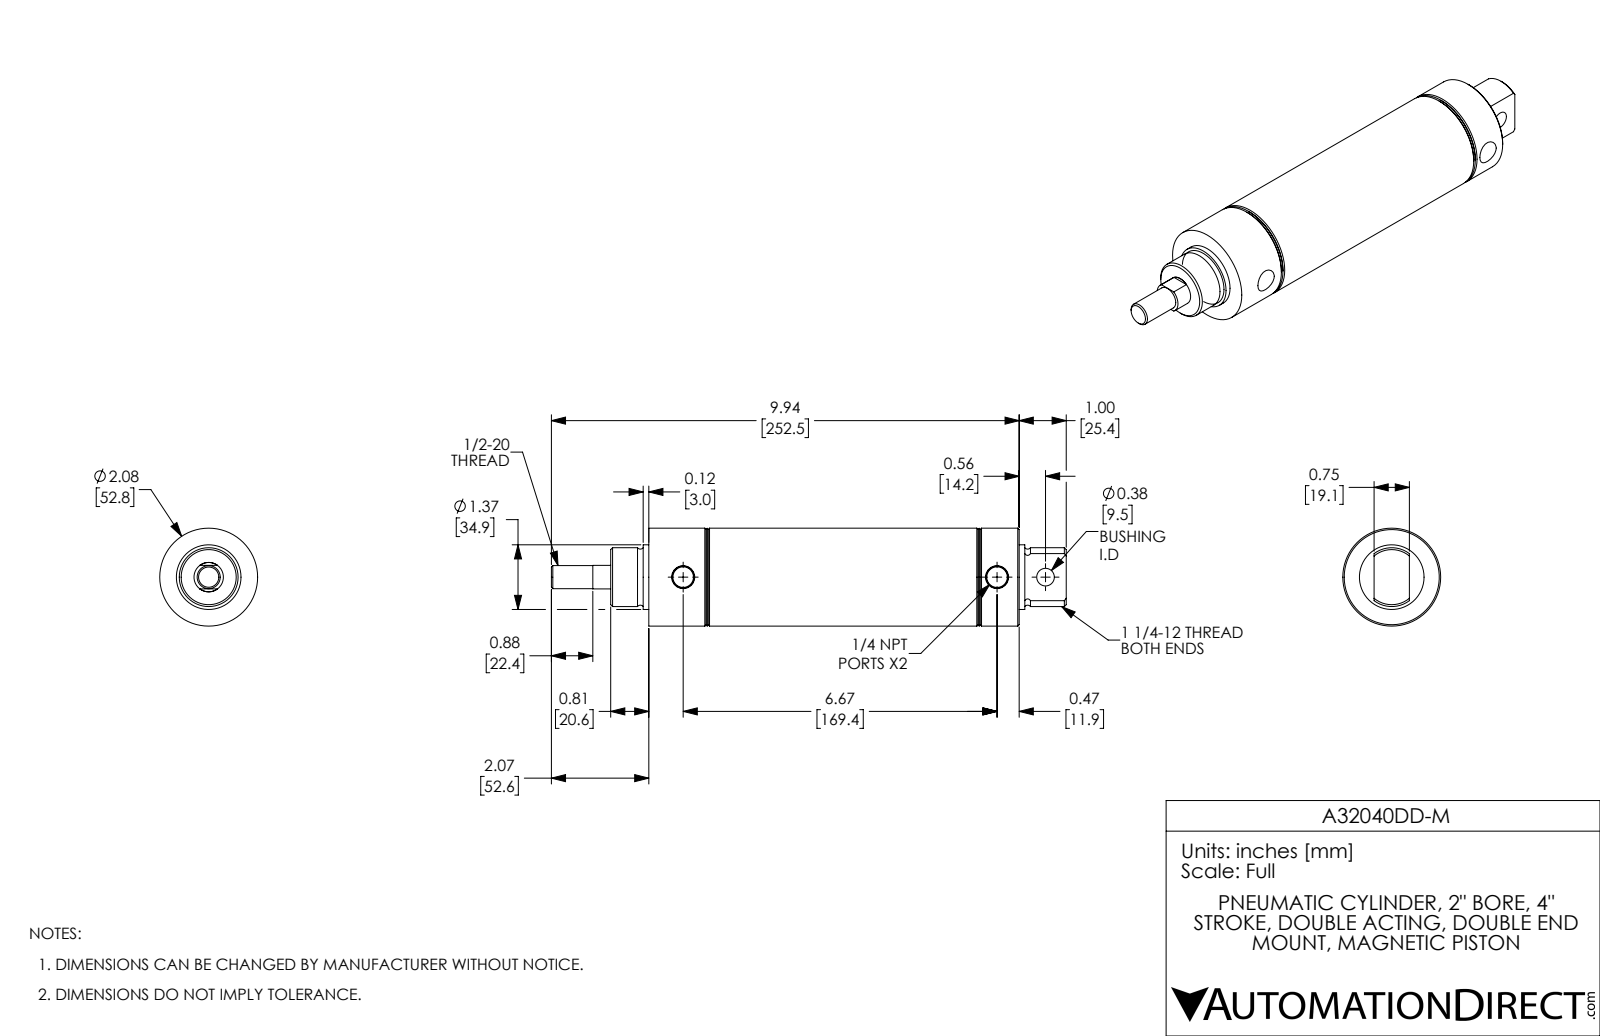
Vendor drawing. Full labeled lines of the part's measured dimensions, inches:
Part name (STEP PRODUCT): A32040DD-M-MainBody; A32040DD-M-Rod; A32040DD-M
STEP written by: SolidWorks 2017 (AUTOMOTIVE_DESIGN)
Units: inches
Bodies: 2 solids, 88 faces (20 planar, 30 cylindrical, 38 other)
Overall size (bounding box): 10.94 × 2.08 × 2.08
Volume: 17.23 in³ · Surface area: 131.4 in²
Round holes (diameter × count): ⌀0.438 ×2, ⌀0.375 ×1, ⌀0.625 ×1, ⌀2 ×1
Round bosses / shafts (diameter × count): ⌀2.08 ×1, ⌀1.373 ×1, ⌀1.25 ×1, ⌀0.491 ×1
Main face-to-face distances: 0.5, 4.5, 4, 6.185, 5.685, 1.685, 1.685, 2.185, 6.185, 7.87
Hole centre spacings: 1.03, 6.67, 7.7
